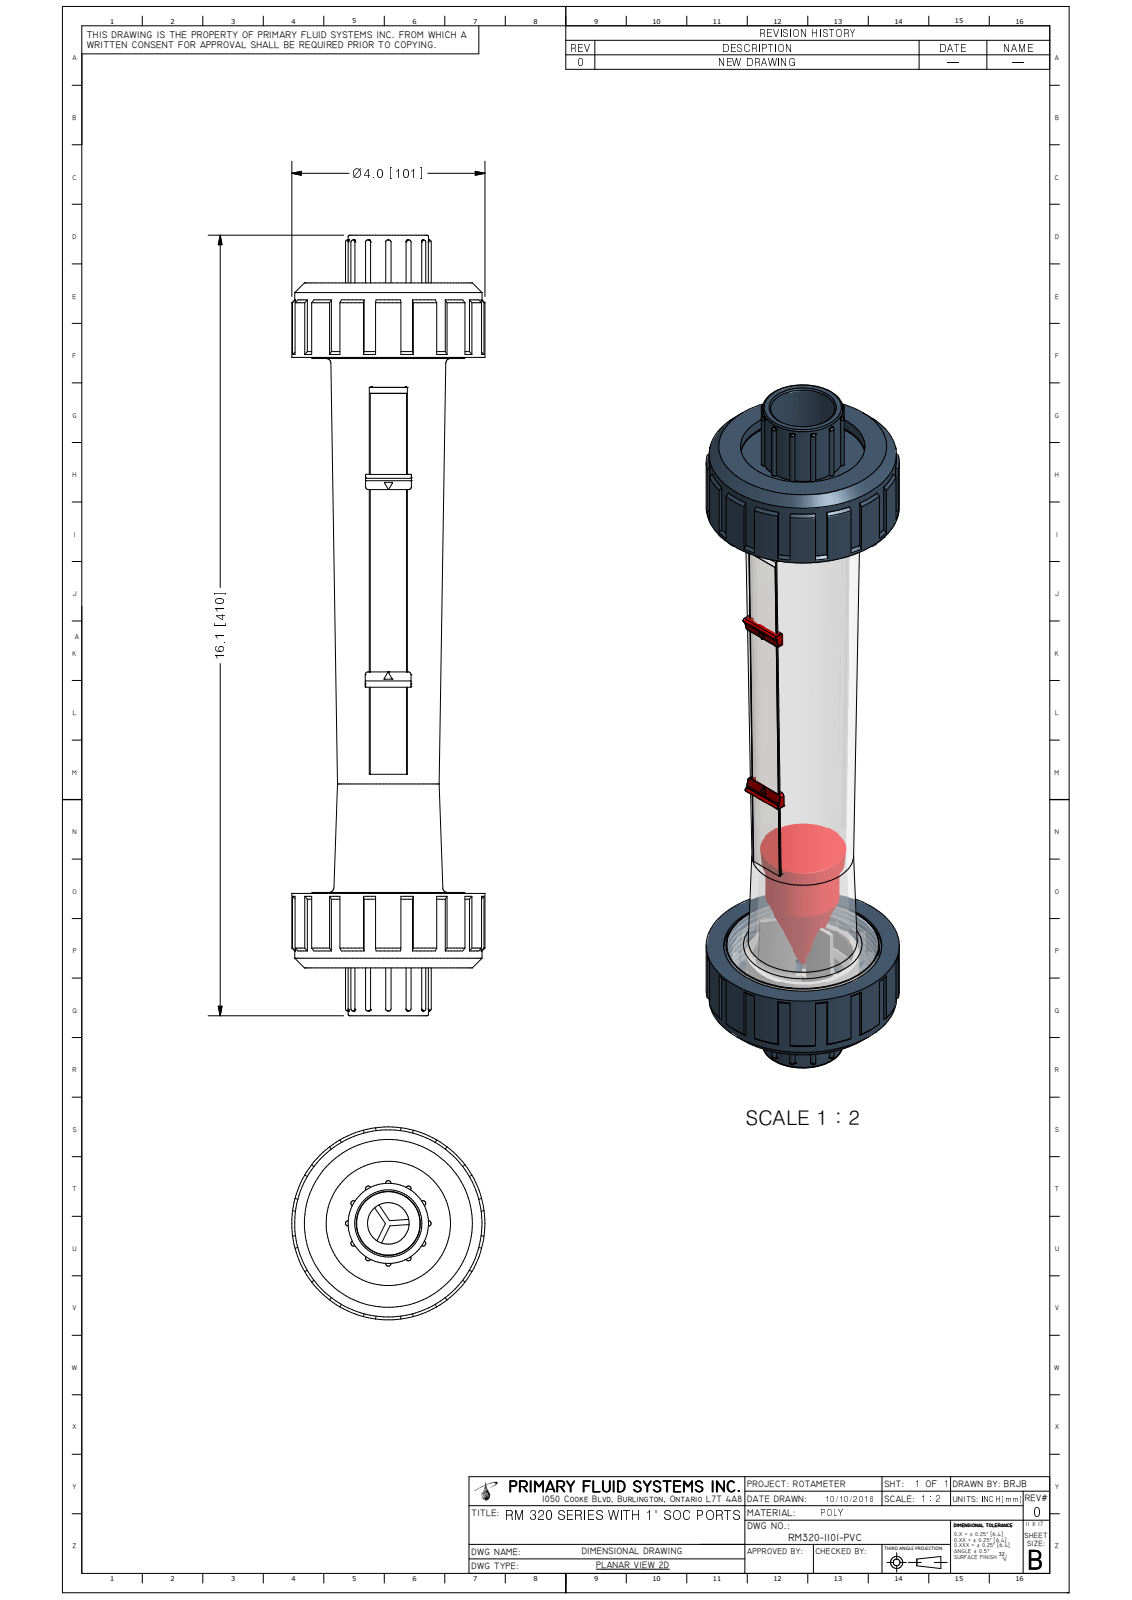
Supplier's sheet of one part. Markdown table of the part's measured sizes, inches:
| quantity | value |
| --- | --- |
| part name | RM320-110I-PVC_R0 |
| STEP written by | Autodesk Inventor 2009 (AUTOMOTIVE_DESIGN) |
| units | inches |
| bodies | 1 solid, 627 faces (213 planar, 128 cylindrical, 286 other) |
| overall size | 16.14 × 3.99 × 3.99 |
| volume | 77.46 in³ |
| surface area | 267.1 in² |
| round holes (diameter × count) | 2.57 × 1, 3.147 × 1, 3.265 × 1, 3.265 × 1 |
| round bosses / shafts (diameter × count) | 3.99 × 1, 3.87 × 1, 3.158 × 1, 2.984 × 1, 1.66 × 1 |
| partial cylindrical surfaces (radius × count) | 0.055 × 24, 0.008 × 18, 0.01 × 16, 0.004 × 8, 0.006 × 8, 0.06 × 4, 0.008 × 2, 0.04 × 2 |
| main face-to-face distances | 1.54, 12.626, 0.3, 13.866, 1.24, 12.326, 1.563, 12.603, 1.263, 12.303 |
